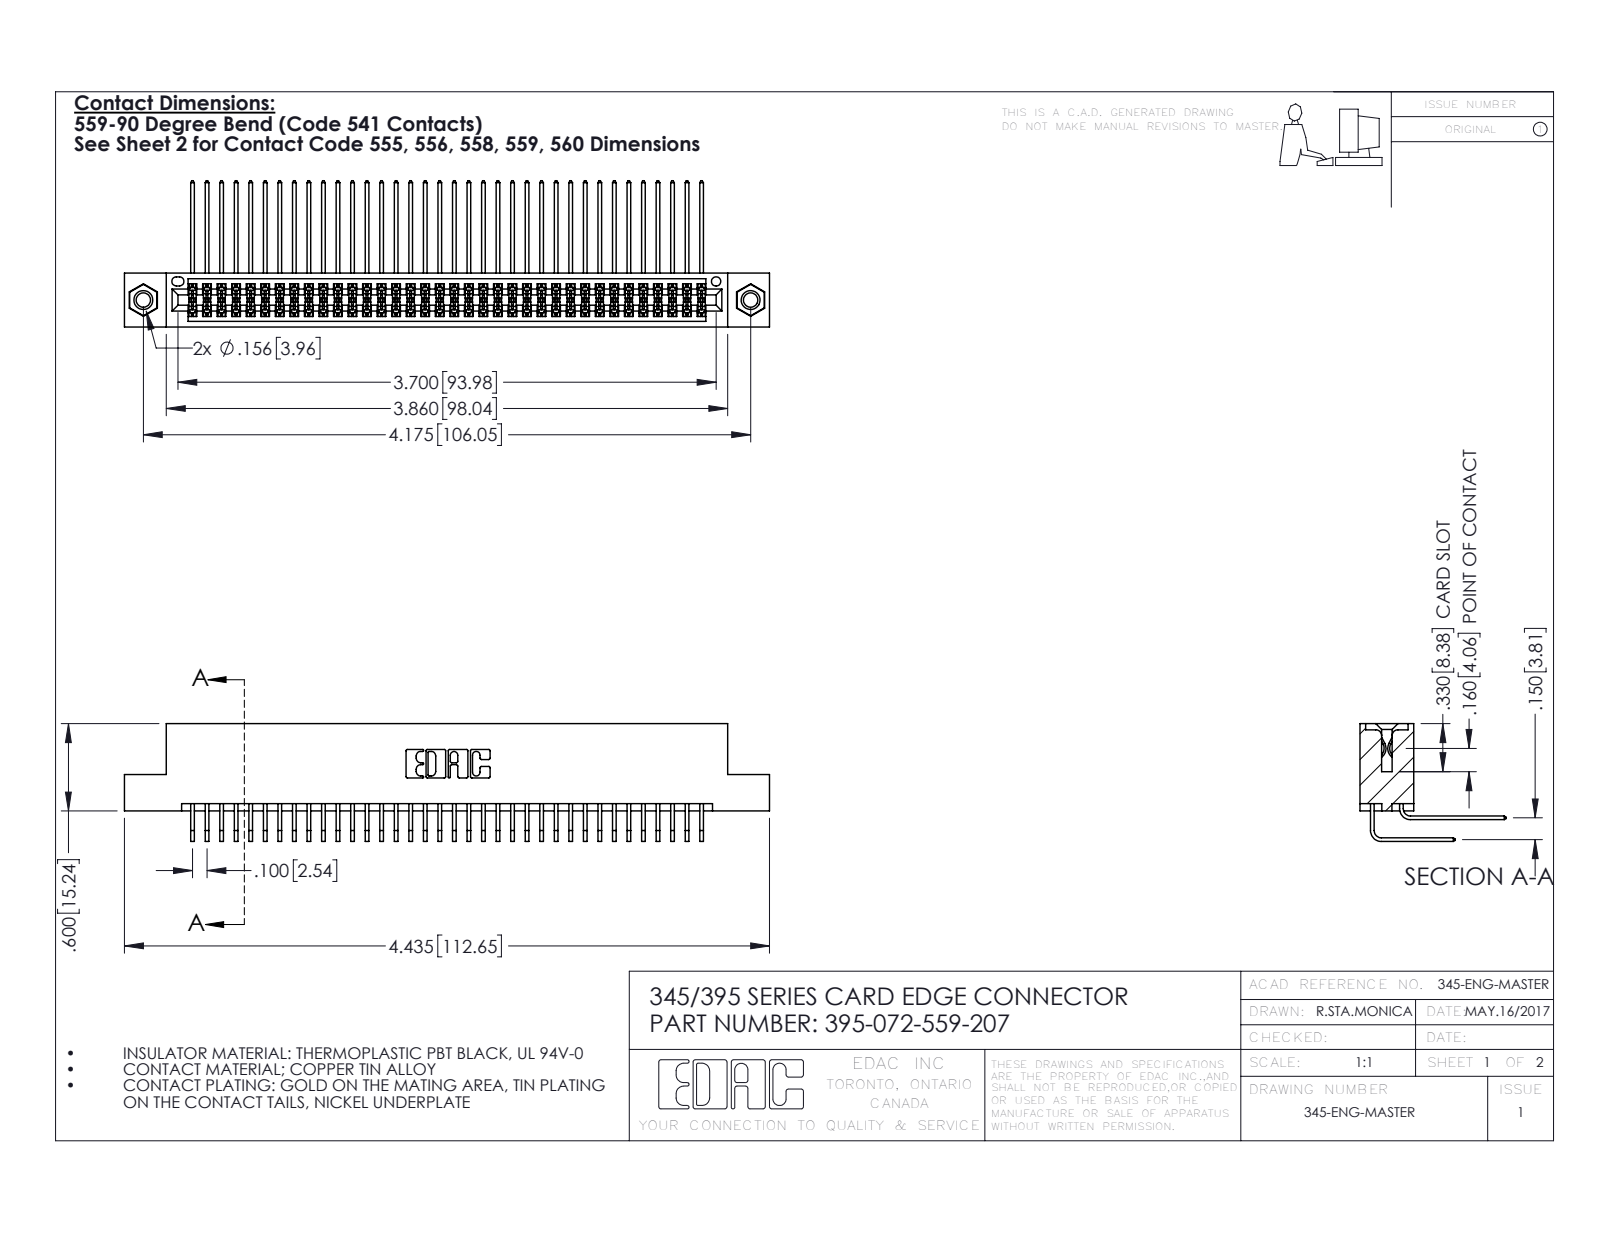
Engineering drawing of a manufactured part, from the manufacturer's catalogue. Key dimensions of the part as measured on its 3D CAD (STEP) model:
Part name (STEP PRODUCT): 345-250-001_345-250-005-103; 345-292-001_558 559 Tail - 1; 345 Part_Flush Mounting Lugs - 0.156 Dia-TI; 395-072-559-207 (+1 more)
STEP written by: SolidWorks 2016 (CONFIG_CONTROL_DESIGN)
Units: inches
Bodies: 75 solids, 3930 faces (2632 planar, 1282 cylindrical, 16 other)
Overall size (bounding box): 4.435 × 1.005 × 0.809
Volume: 0.689 in³ · Surface area: 28.76 in²
Round holes (diameter × count): ⌀0.098 ×2, ⌀0.125 ×2, ⌀0.156 ×2, ⌀0.064 ×1
Round bosses / shafts (diameter × count): ⌀0.155 ×2
Partial cylindrical surfaces — rounded edges, fillets, slot ends (radius × count): R0.006 ×108, R0.01 ×22, R0.007 ×6, R0.031 ×6, R0.026 ×3, R0.014 ×2, R0.019 ×2, R0.022 ×2
Main face-to-face distances: 0.072, 0.298, 0.2, 0.37, 0.098, 0.272, 0.025, 0.225, 0.175, 0.15
Hole centre spacings: 0.27, 3.939, 4.175
